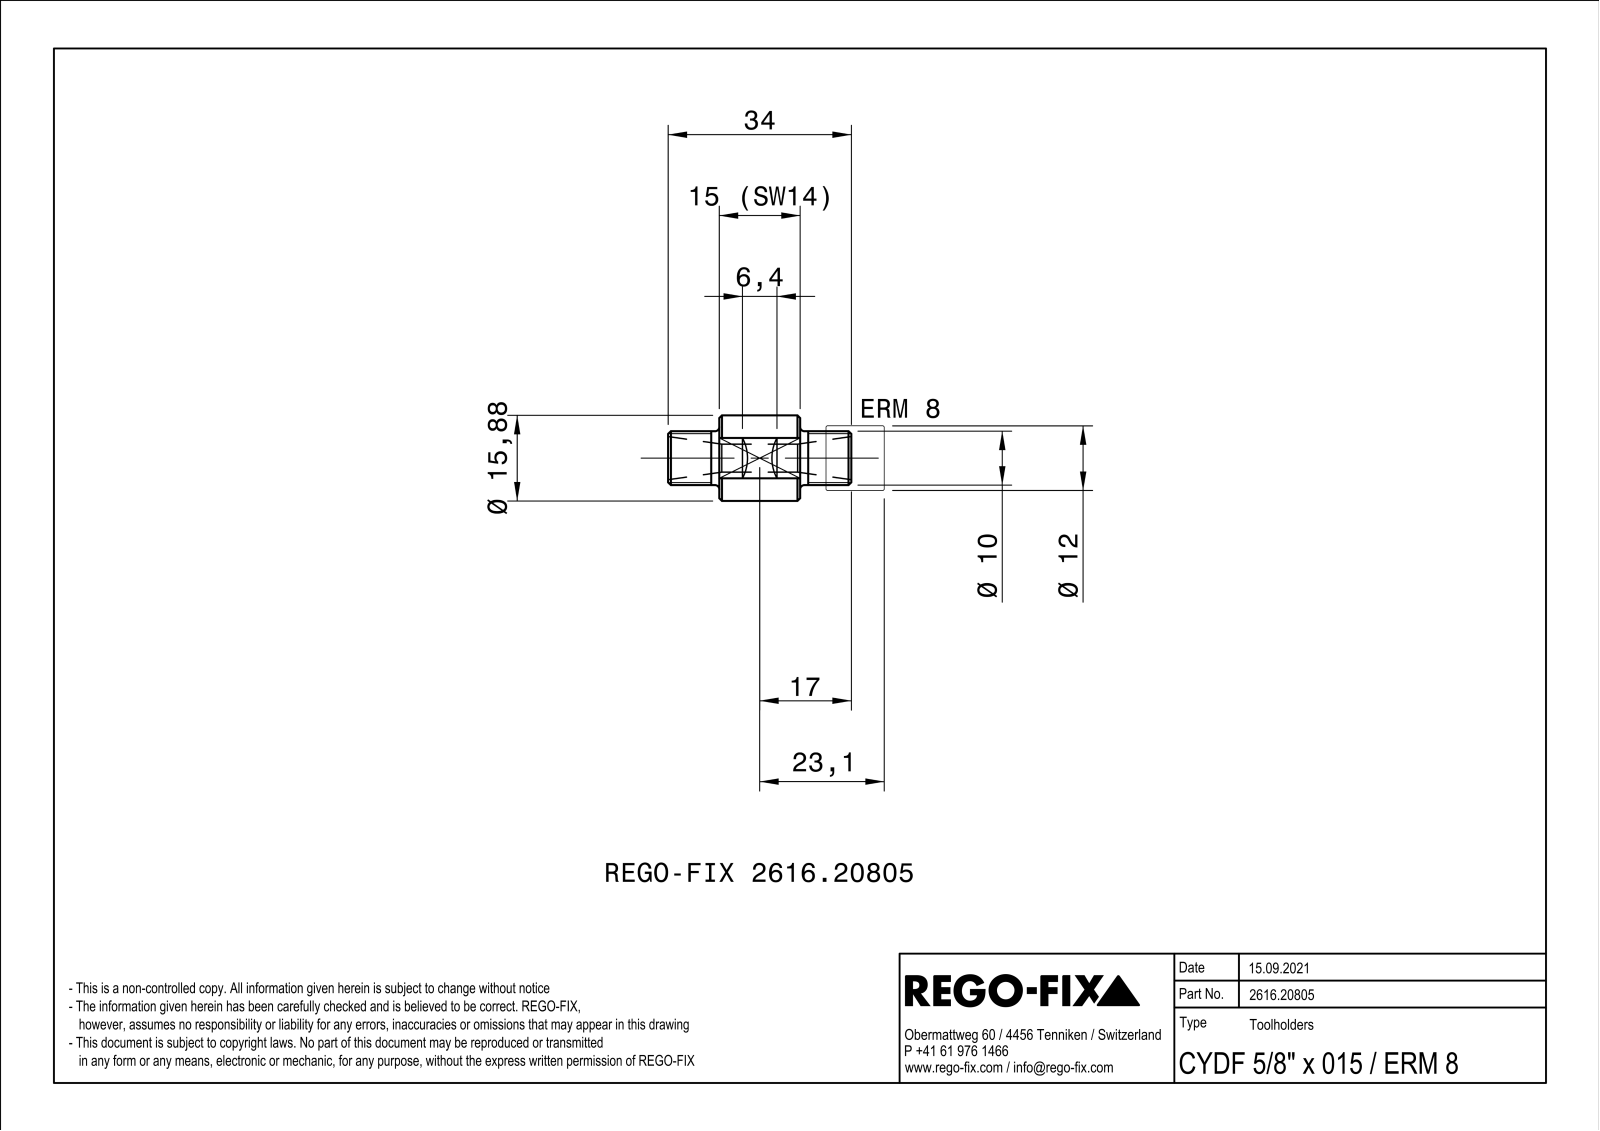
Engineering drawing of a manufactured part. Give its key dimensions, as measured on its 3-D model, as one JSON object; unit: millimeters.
{"part_name": "NOCUT", "step_written_by": "SIEMENS PLM Software Solid Edge ST10 (AUTOMOTIVE_DESIGN)", "units": "millimeters", "bodies": {"solids": 1, "faces": 31, "planar": 13, "cylindrical": 6, "other": 12}, "overall_size": [34, 15.88, 14.94], "volume_mm3": 3345, "surface_area_mm2": 2194, "round_holes": [[5.2, 1]], "round_bosses_or_shafts": [[15.88, 1], [10, 1]], "face_to_face_distances": [15, 14, 9.5, 24.5, 34, 2.79, 20, 17.21]}
